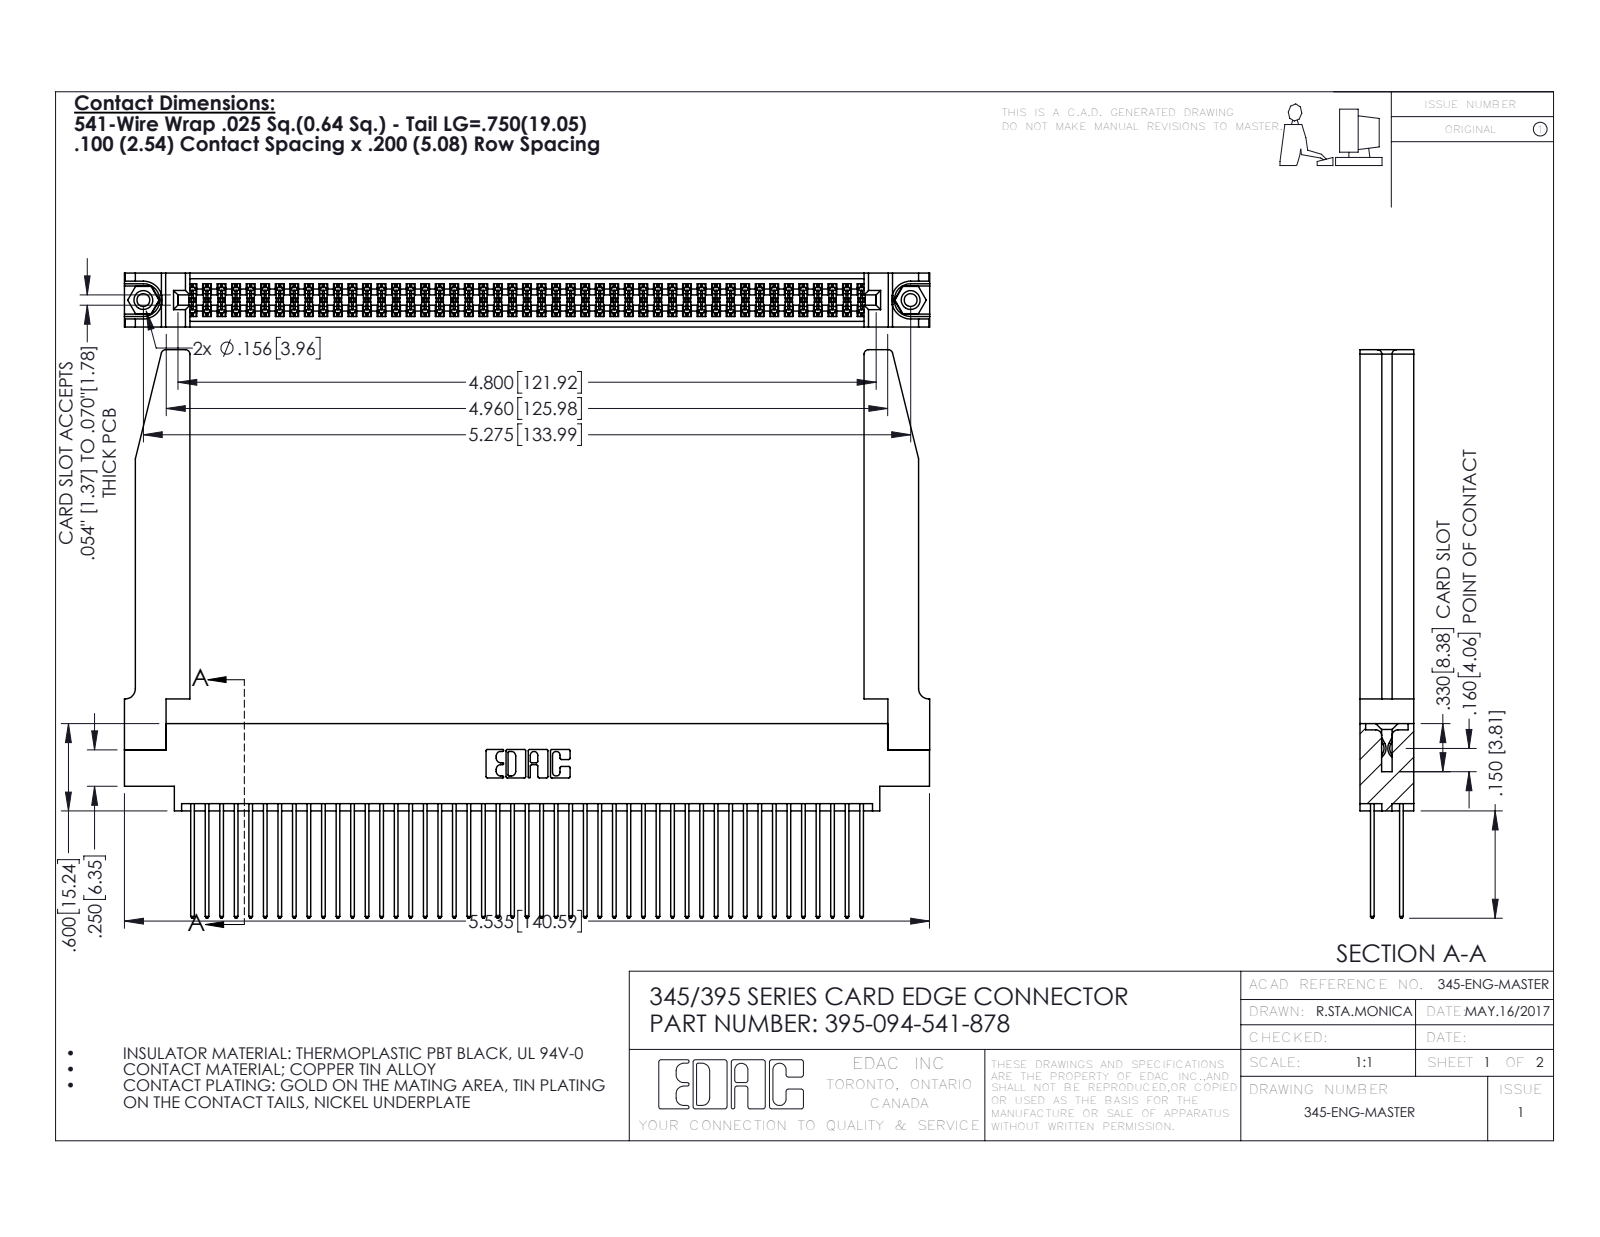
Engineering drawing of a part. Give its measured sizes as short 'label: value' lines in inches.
name: 345-220-078_345-220-078; 395-094-541-878; 345-250-001_345-250-001-102; 345 Part_0.170 Offset - 0.156 Dia-TH (+1 more)
written by: SolidWorks 2016 (CONFIG_CONTROL_DESIGN)
unit: in
bodies: 99 solids, 5064 faces (3328 planar, 1684 cylindrical, 52 other)
size: 5.536 × 3.907 × 0.37
volume: 1.337 in³; area: 47.28 in²
holes: 2× ⌀0.089, 2× ⌀0.125, 2× ⌀0.156, 1× ⌀0.064
bosses: 2× ⌀0.155
rounds: 141× R0.006, 94× R0.01, 22× R0.01, 8× R0.03, 6× R0.007, 6× R0.031, 3× R0.026, 2× R0.014
face distances: 0.072, 0.298, 0.37, 0.098, 0.272, 0.025, 0.2, 0.225, 0.175, 0.148
hole spacings: 0.27, 5.039, 5.275
